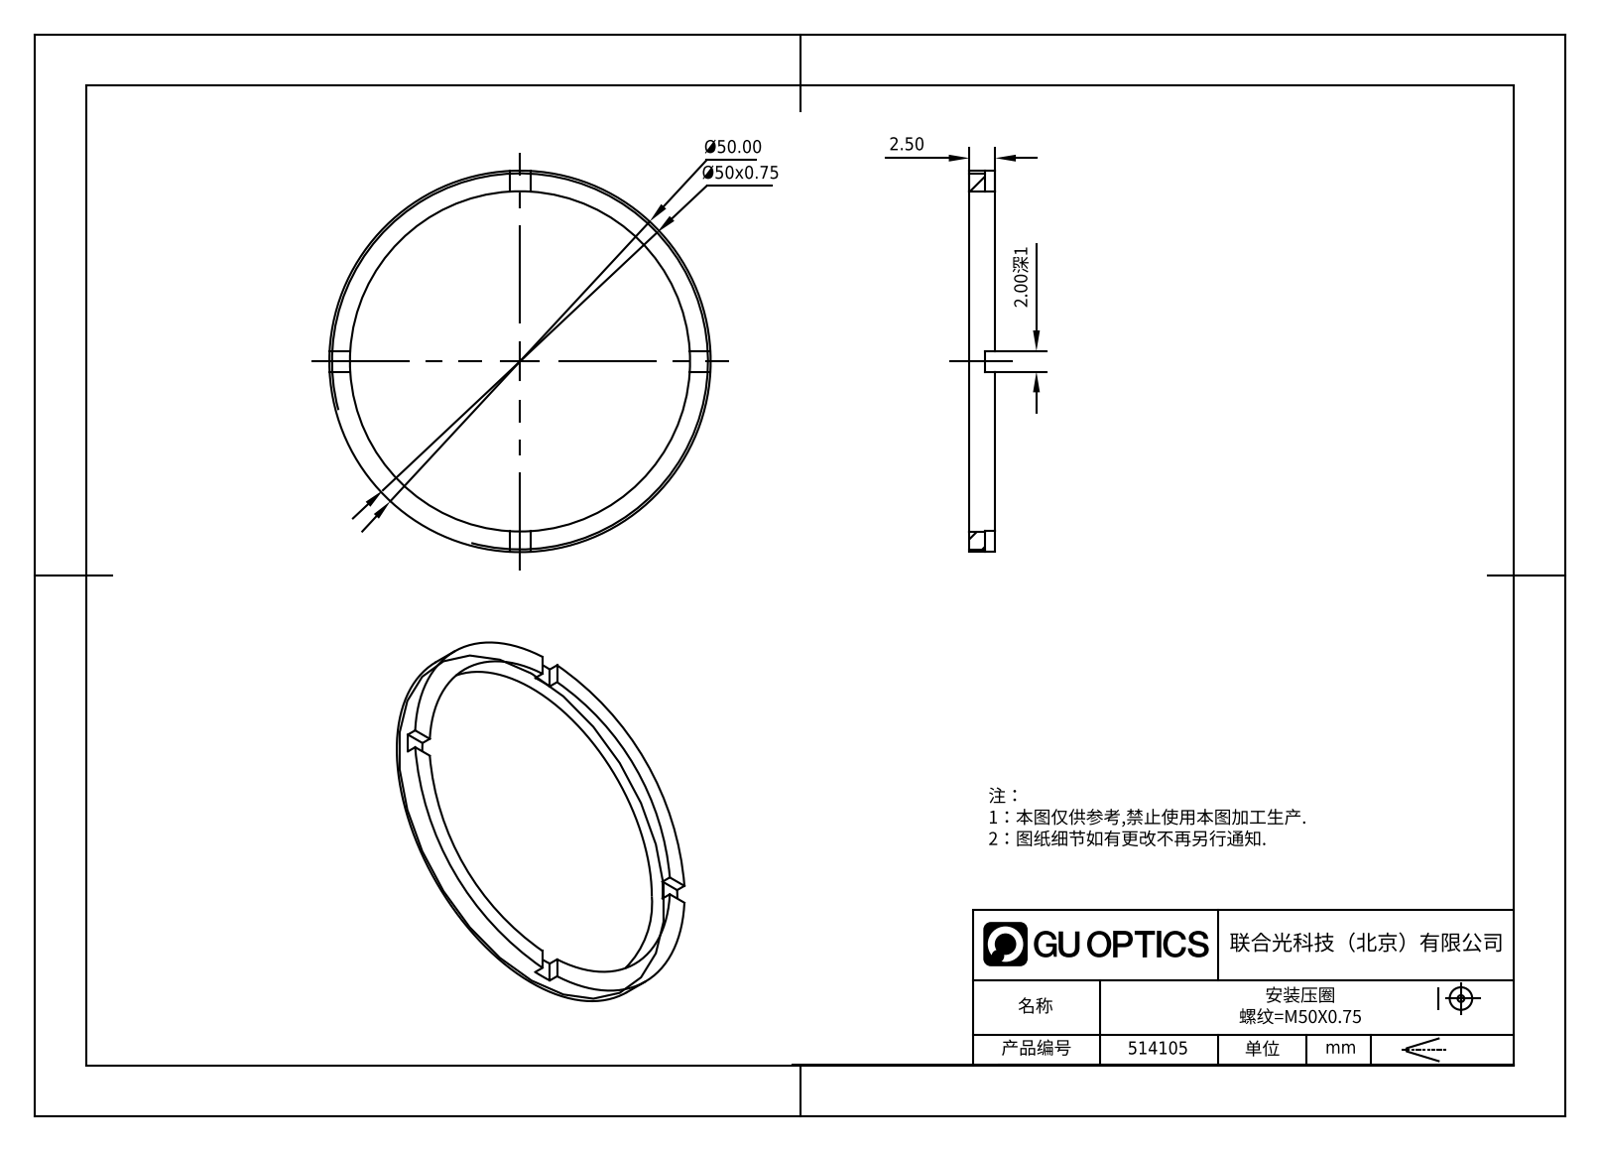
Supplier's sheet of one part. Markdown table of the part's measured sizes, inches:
| quantity | value |
| --- | --- |
| part name | 514105 |
| STEP written by | SolidWorks 2020 (CONFIG_CONTROL_DESIGN) |
| units | inches |
| bodies | 1 solid, 21 faces (17 planar, 4 cylindrical, 0 other) |
| overall size | 1.969 × 1.969 × 0.098 |
| volume | 0.056 in³ |
| surface area | 2.319 in² |
| round holes (diameter × count) | 1.772 × 1 |
| round bosses / shafts (diameter × count) | 1.969 × 1 |
| main face-to-face distances | 0.098, 0.059, 0.039, 0.079 |
